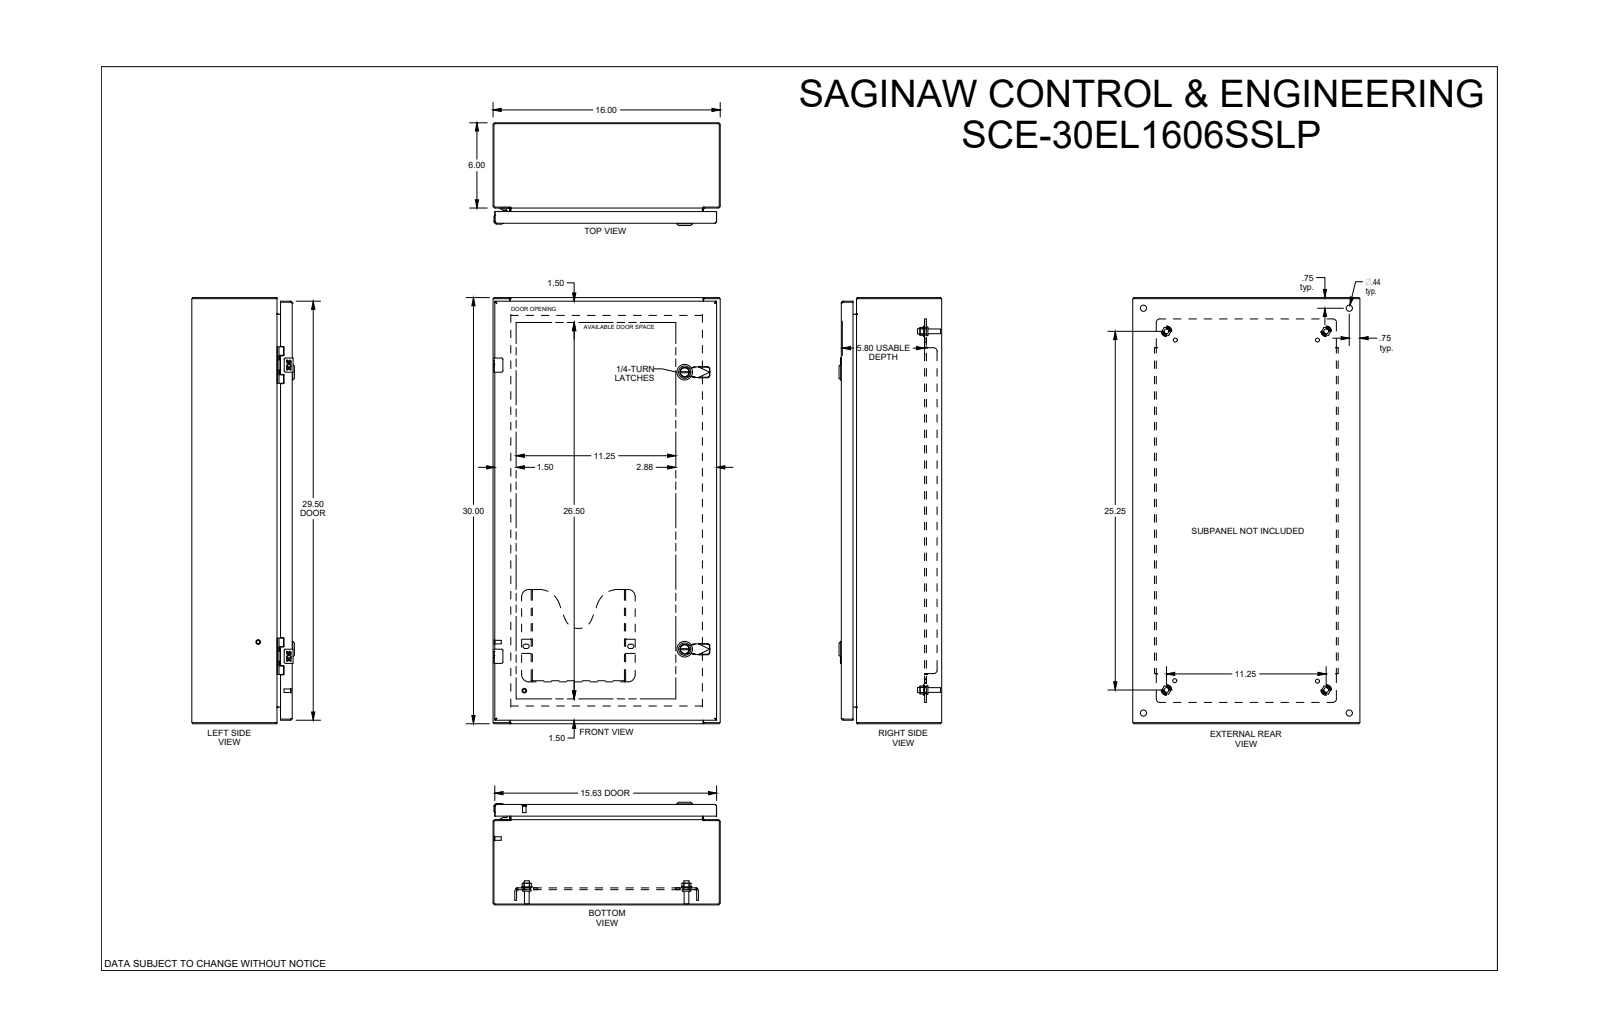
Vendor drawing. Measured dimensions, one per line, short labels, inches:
name: SCE-30EL1606SSLP
written by: SolidWorks 2019 (CONFIG_CONTROL_DESIGN)
unit: in
bodies: 0 solids, 2806 faces (1297 planar, 749 cylindrical, 760 other)
size: 30 × 16 × 7.23
holes: 4× ⌀0.172, 4× ⌀0.205, 4× ⌀0.244, 4× ⌀0.266, 4× ⌀0.281, 4× ⌀0.367, 4× ⌀0.437, 4× ⌀0.5, 3× ⌀0.375, 2× ⌀0.156, 2× ⌀0.197, 2× ⌀0.218
bosses: 6× ⌀0.17, 4× ⌀0.366, 4× ⌀0.332, 4× ⌀0.25, 4× ⌀0.248, 3× ⌀0.196, 2× ⌀1.102, 2× ⌀0.866
rounds: 56× R0.012, 32× R0.015, 28× R0.01, 23× R0.04, 20× R0.02, 12× R0.029, 10× R0.07, 10× R0.145
face distances: 0.075, 0.075, 6.923, 6.998, 7.073, 6.998, 0.125, 1, 1.125, 5.923
hole spacings: 20.5, 0.985, 0.02, 2.298, 4.493, 12.978, 26.924, 29.8
